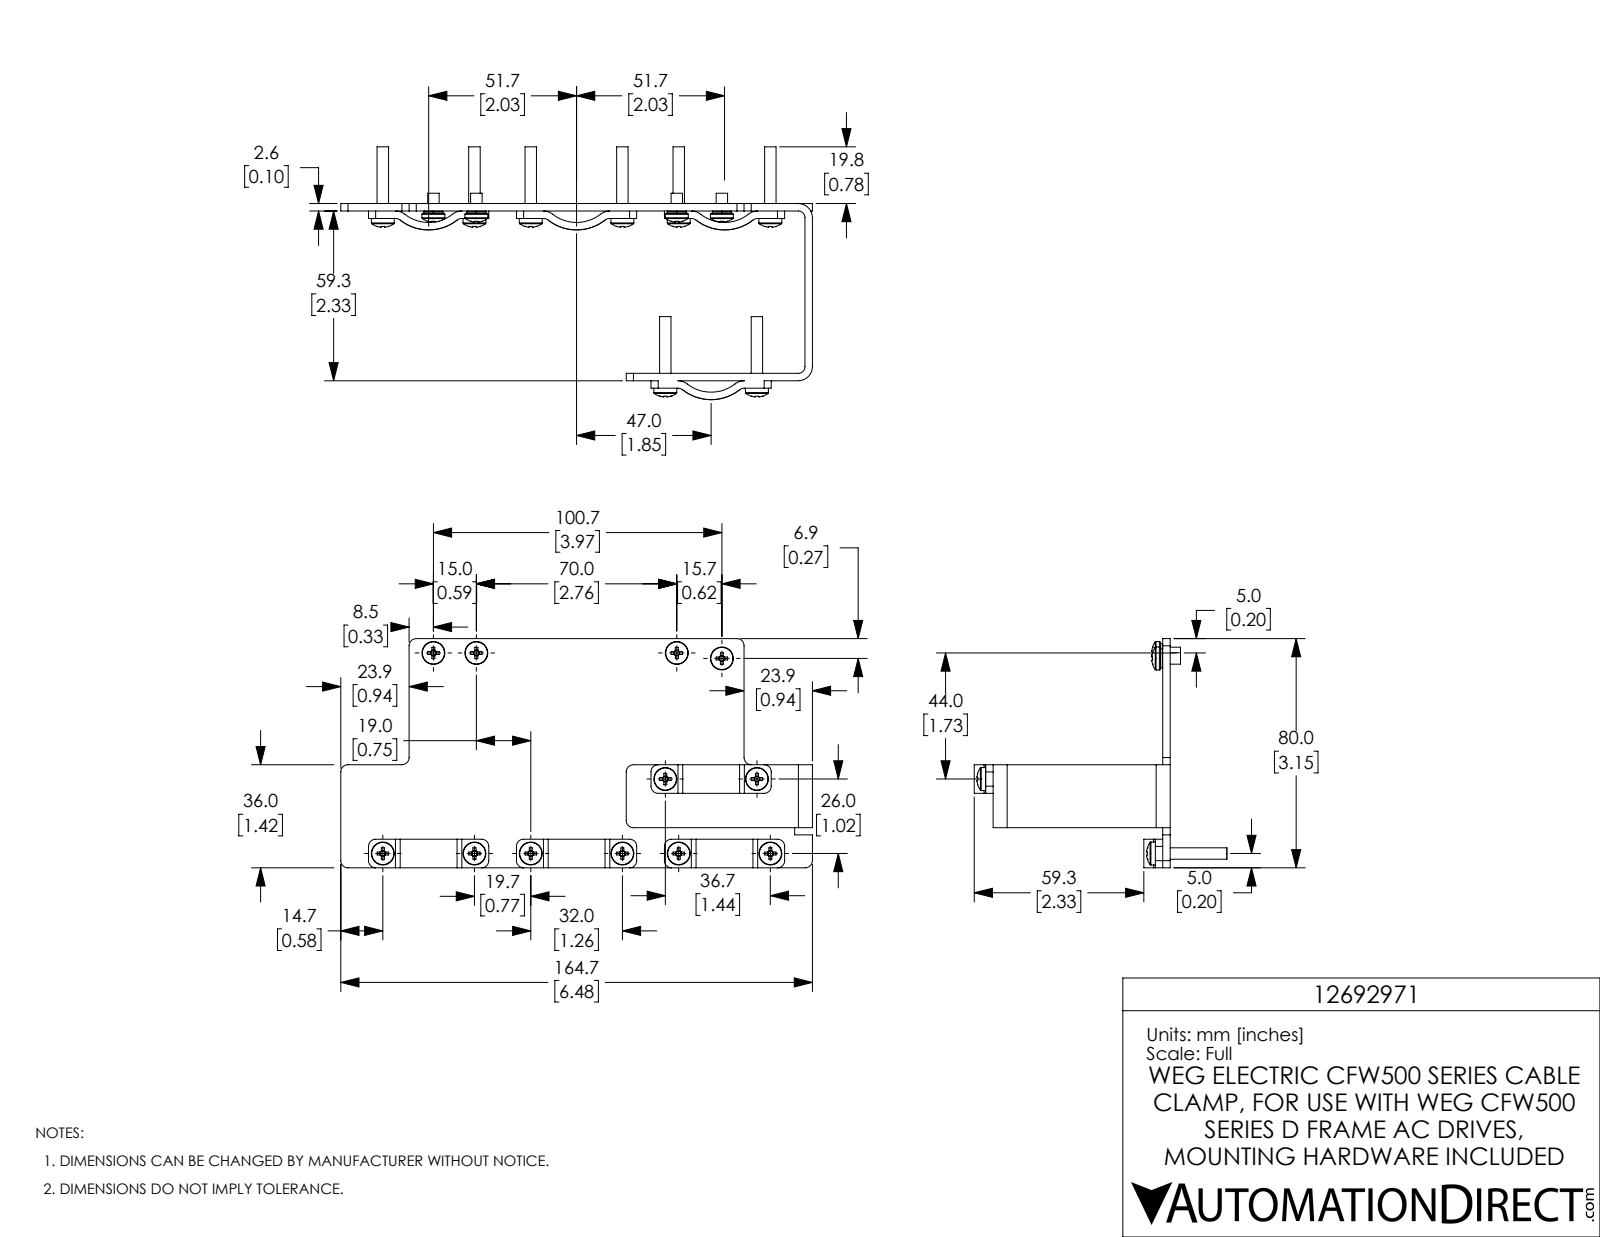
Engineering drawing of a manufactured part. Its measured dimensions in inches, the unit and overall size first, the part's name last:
Units: inches
Overall size (bounding box): 6.484 × 3.474 × 3.15
Round holes (diameter × count): ⌀0.177 ×10, ⌀0.148 ×4, ⌀0.13 ×1
Round bosses / shafts (diameter × count): ⌀0.315 ×12, ⌀0.157 ×12, ⌀0.26 ×4, ⌀0.126 ×4
Partial cylindrical surfaces — rounded edges, fillets, slot ends (radius × count): R0.098 ×25, R0.106 ×8, R0.209 ×8, R0.531 ×4, R0.634 ×4, R0.091 ×2, R0.193 ×2, R0.065 ×1
Main face-to-face distances: 0.102, 2.333, 2.23, 2.435, 1.417, 1.024, 0.394, 0.205, 0.551, 0.866
Hole centre spacings: 1.26, 2.034, 2.756, 0.774, 1.04, 2.114, 2.856, 3.041
Volume: 2.655 in³ · Surface area: 56.6 in²
Bodies: 1 solid, 628 faces (283 planar, 174 cylindrical, 171 other)
Part name (STEP PRODUCT): ZBC_100061244482 nc cmb1
STEP written by: SolidWorks 2017 (AUTOMOTIVE_DESIGN)
